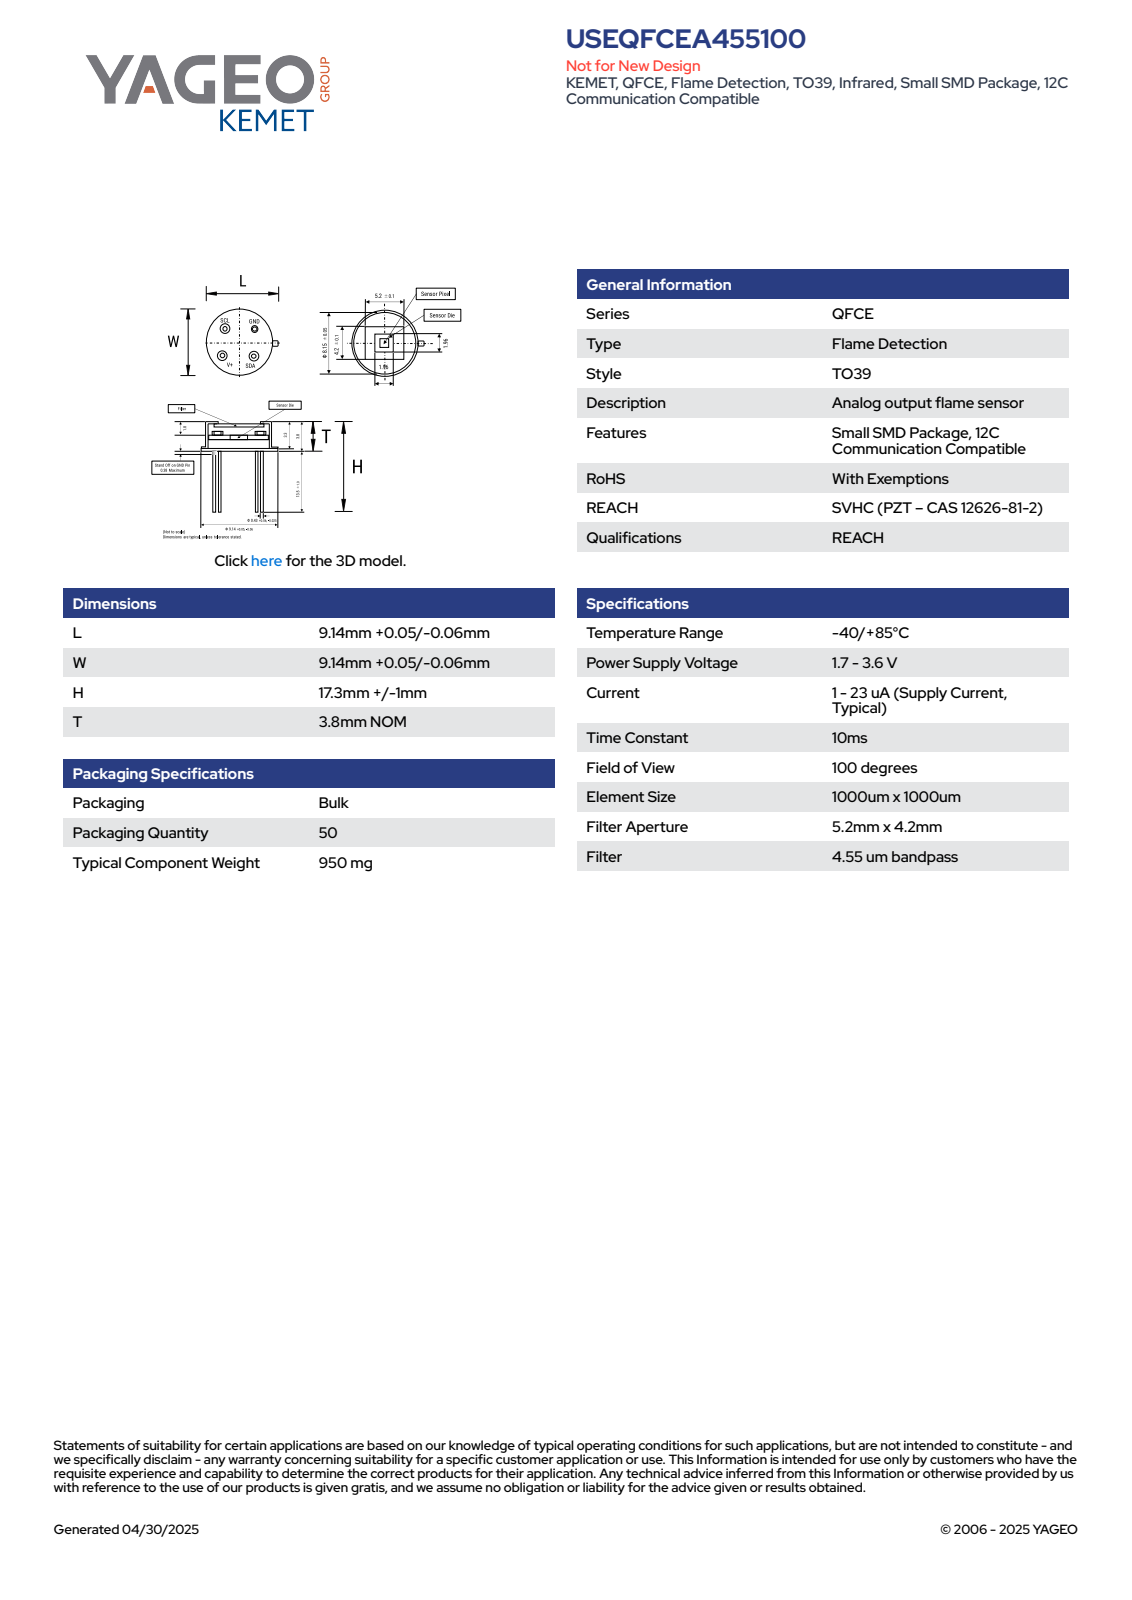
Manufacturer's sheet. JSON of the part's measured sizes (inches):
{"part_name": "SF_QFCE_L9.19H18.3T3.8W9.19", "step_written_by": "SolidWorks 2020 (AUTOMOTIVE_DESIGN)", "units": "inches", "bodies": {"solids": 1, "faces": 82, "planar": 69, "cylindrical": 13, "other": 0}, "overall_size": [0.72, 0.381, 0.362], "volume_in3": 0.013, "surface_area_in2": 0.484, "round_bosses_or_shafts": [[0.017, 4], [0.362, 1], [0.323, 1]], "face_to_face_distances": [0.15, 0.149, 0.02, 0.13, 0.13, 0.571, 0.591, 0.72, 0.72, 0.093]}
